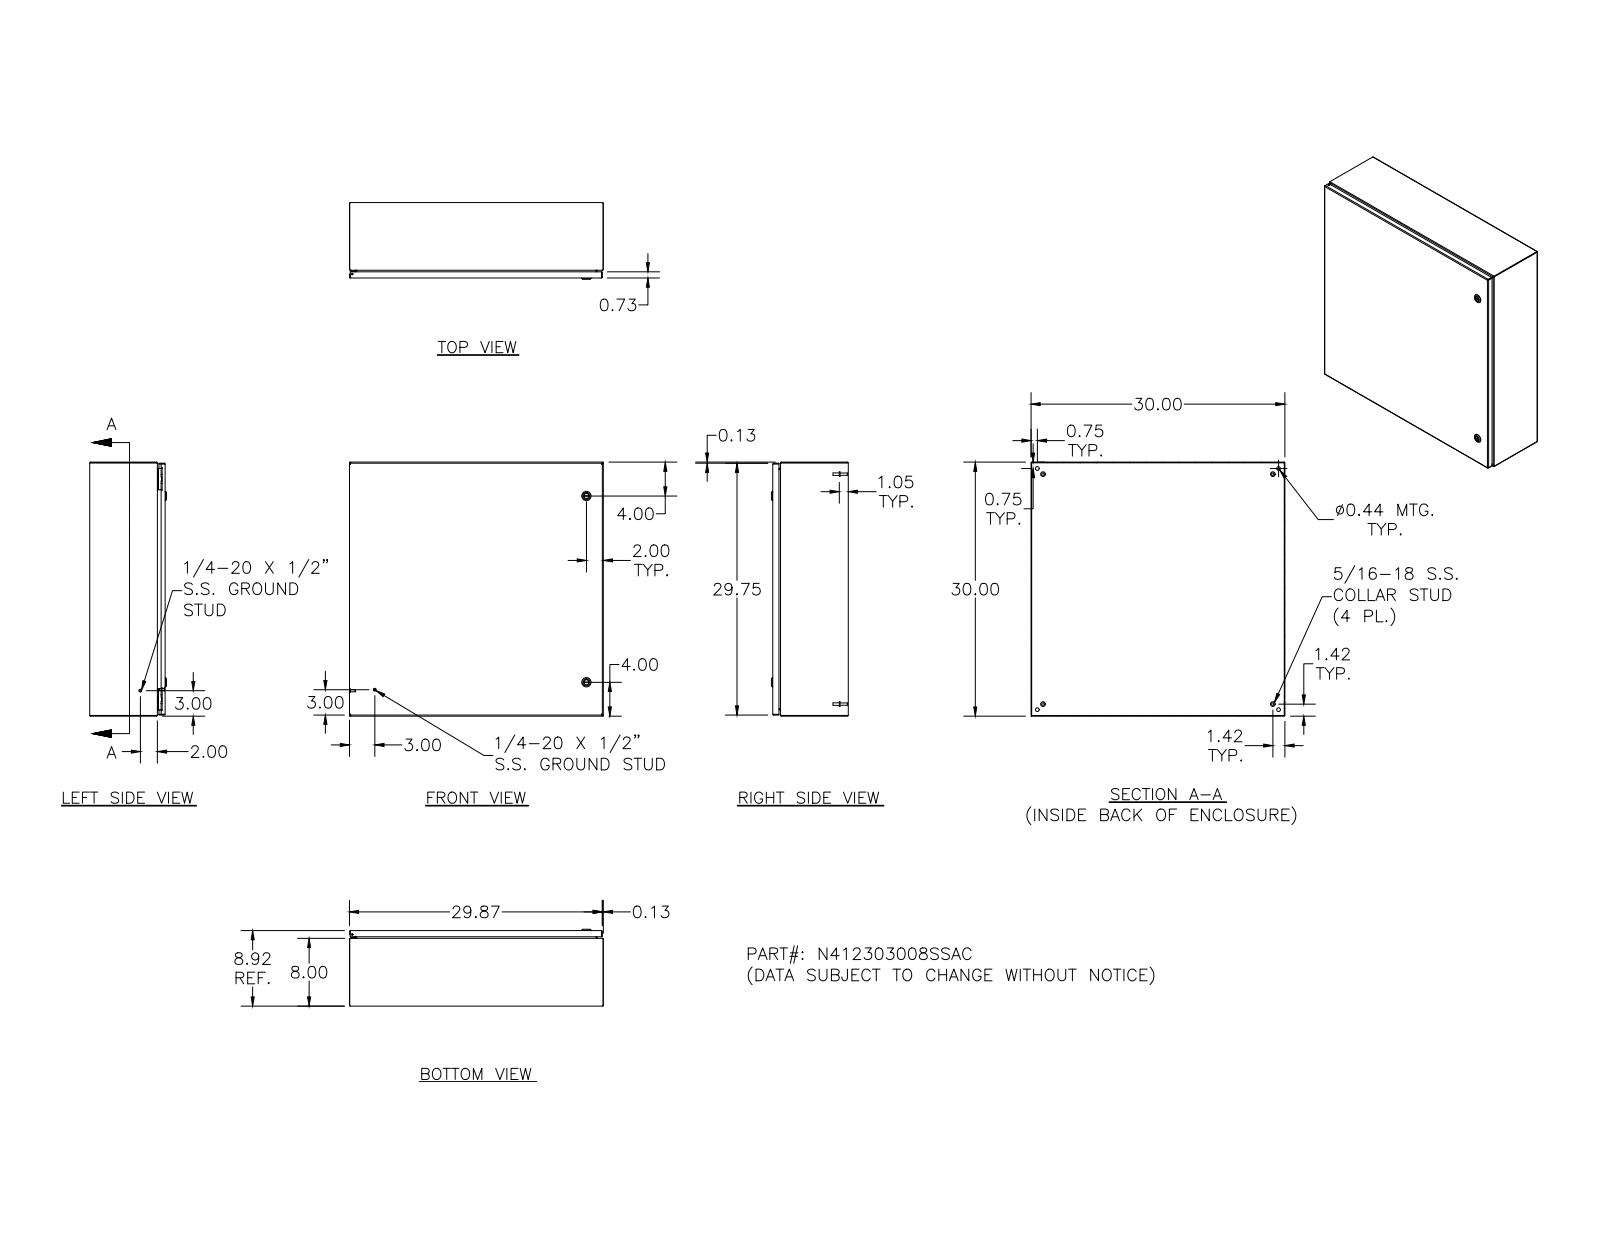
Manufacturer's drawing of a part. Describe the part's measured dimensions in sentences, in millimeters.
The part is named "N412303008SSAC; N412303008SSACBKP; 388151; N4123030SSACLID (+8 more)". Its 3-D file was written by "Autodesk Inventor 2011 (AUTOMOTIVE_DESIGN)". It is 42 solids with 1662 faces: 698 planar, 588 cylindrical and 376 other. Overall it measures 762 by 762 by 230.5 millimeters. Its volume is 3 644 000 cubic millimeters and its surface area 3 892 000 square millimeters. Round holes: 5 of diameter 4.8, 4 of diameter 2.4, 4 of diameter 3.9, 4 of diameter 4.2, 4 of diameter 4.4, 4 of diameter 11.1, 2 of diameter 4, 2 of diameter 5, 2 of diameter 8, 2 of diameter 10, 2 of diameter 10.2, 2 of diameter 16.1. Round bosses or shafts: 10 of diameter 6.4, 4 of diameter 14.3, 4 of diameter 9.1, 4 of diameter 8.1, 4 of diameter 7.6, 4 of diameter 7, 4 of diameter 6.5, 4 of diameter 4.2. Partial cylindrical surfaces (rounded edges, fillets, slot ends): 26 of radius 1.3, 18 of radius 0.4, 16 of radius 0.4, 16 of radius 2.3, 15 of radius 0.5, 14 of radius 0.8, 14 of radius 3.2, 8 of radius 0.8. The main face-to-face distances are 1.9, 224.6, 760.1, 226.5, 222.7, 758.2, 762, 201.3, 23.3, 18.8. The hole center spacings are 660.4, 0.4, 16.8, 723.9, 703.5, 0.5, 12.7, 16.5.
